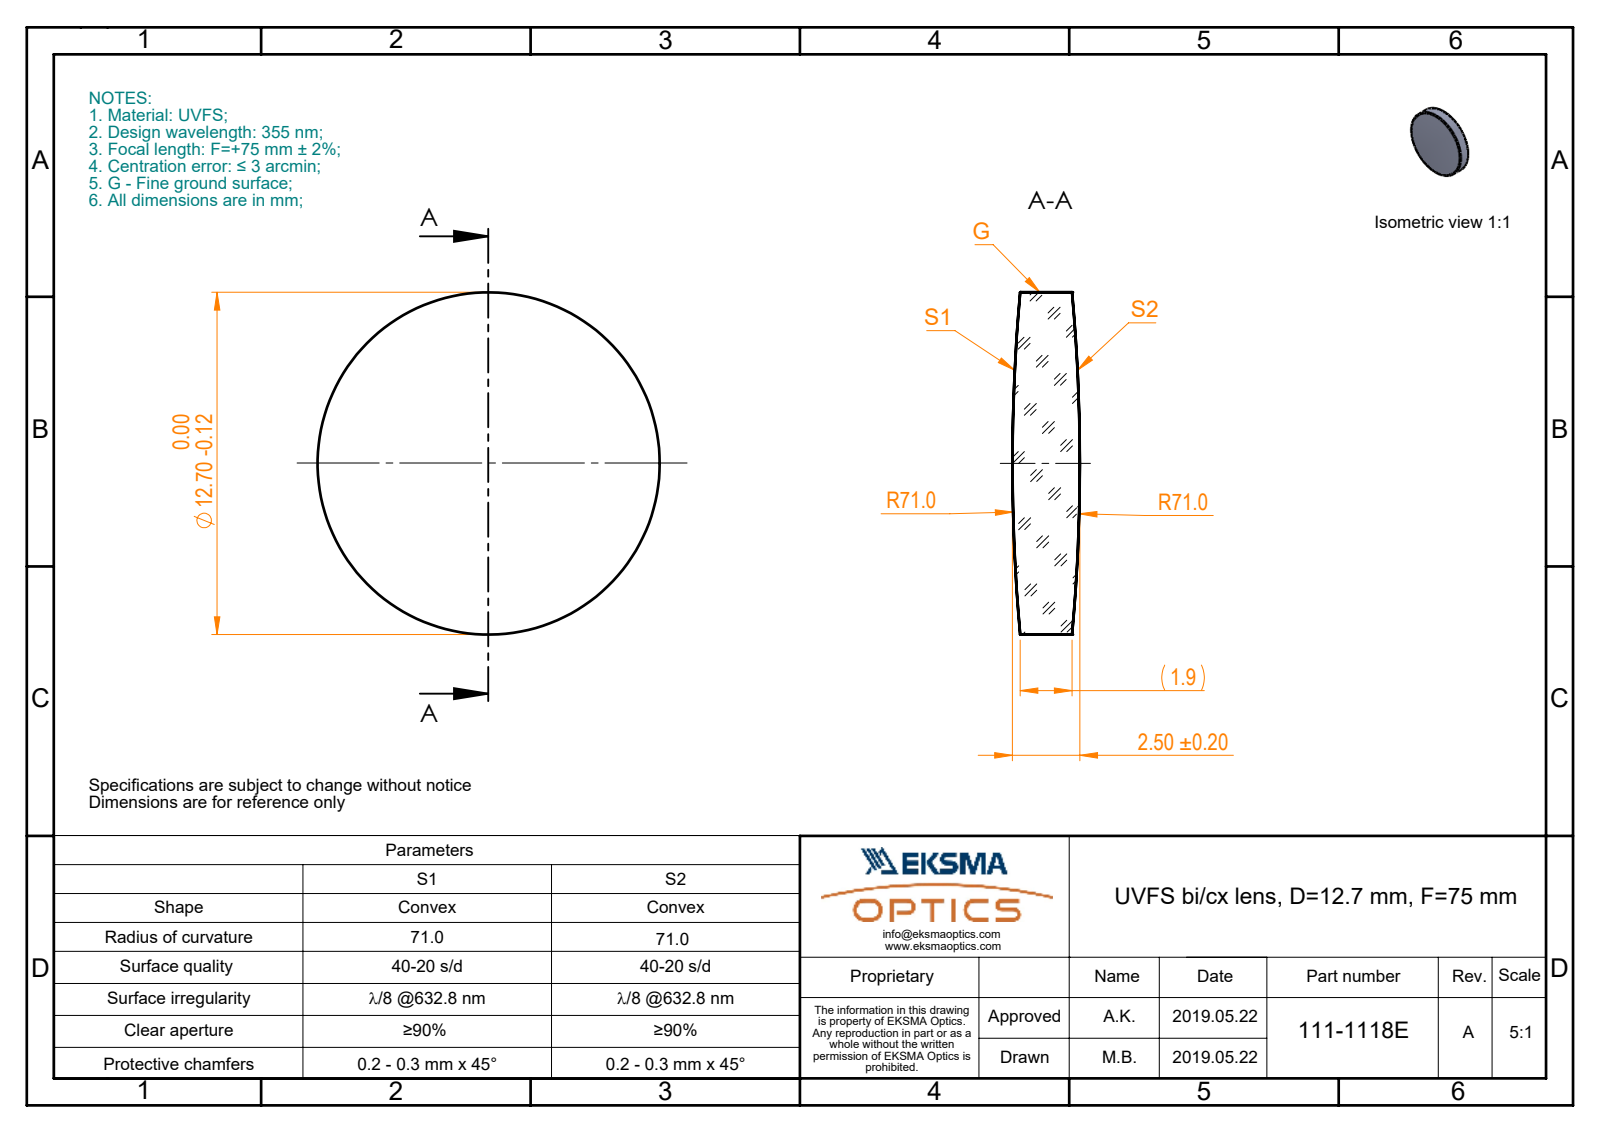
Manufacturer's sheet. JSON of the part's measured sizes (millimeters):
{"part_name": "111-1118E UVFS bi-cx 12.7 F75", "step_written_by": "SolidWorks 2017 (CONFIG_CONTROL_DESIGN)", "units": "millimeters", "bodies": {"solids": 1, "faces": 6, "planar": 0, "cylindrical": 2, "other": 4}, "overall_size": [12.7, 12.7, 2.5], "volume_mm3": 281, "surface_area_mm2": 331, "round_bosses_or_shafts": [[12.7, 1]]}
